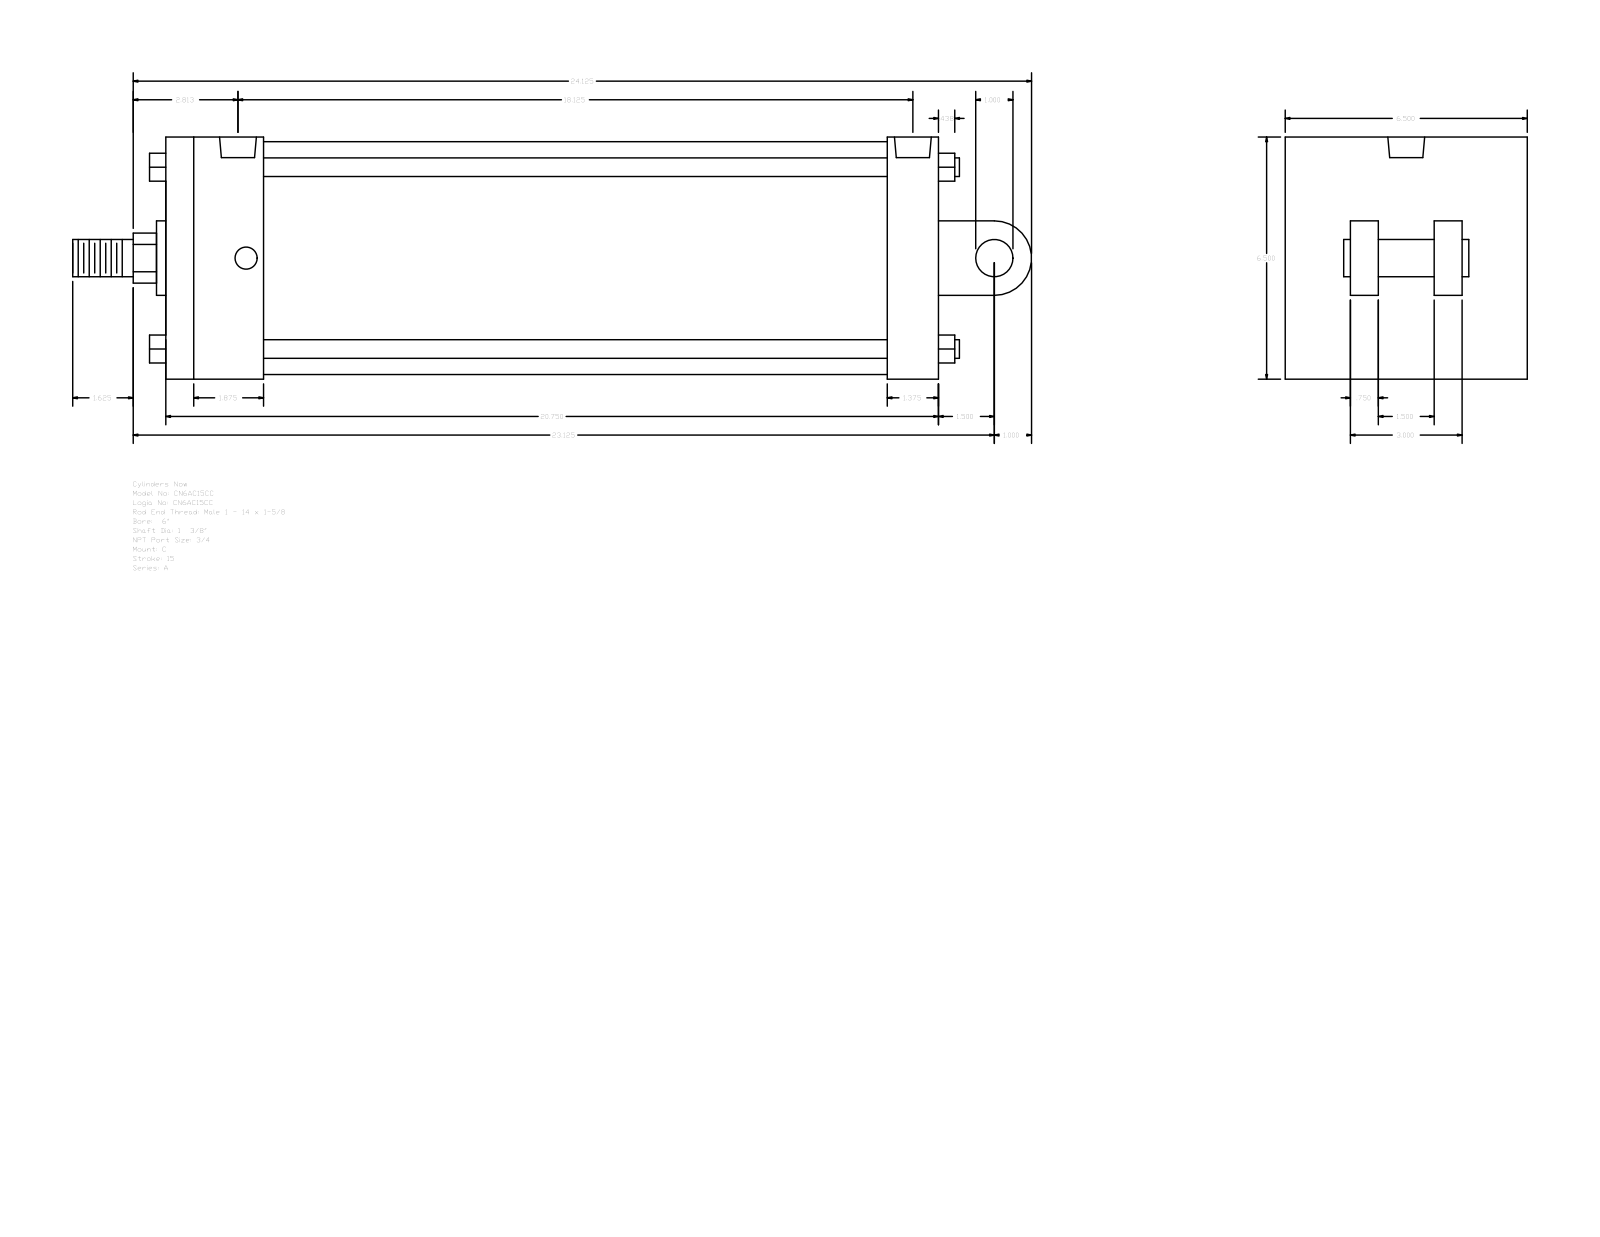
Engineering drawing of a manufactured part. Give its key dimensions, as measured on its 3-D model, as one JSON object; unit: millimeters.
{"part_name": "A_C__0600_1.375", "step_written_by": "GSSL Pune (CONFIG_CONTROL_DESIGN)", "units": "millimeters", "bodies": {"solids": 0, "faces": 135, "planar": 102, "cylindrical": 33, "other": 0}, "overall_size": [654.05, 165.1, 165.1], "round_holes": [[15.08, 4], [25.12, 2]], "round_bosses_or_shafts": [[12.7, 4], [25.4, 2], [158.75, 1], [50.8, 1], [34.92, 1]], "partial_cylinders_radius": [[17.06, 1], [25.4, 1]], "face_to_face_distances": [165.1, 527.04, 57.15, 19.05, 66.67, 460.37, 492.12, 425.45, 34.92, 63.5], "hole_center_spacings": [5.56, 449.25, 454.81, 460.37]}
